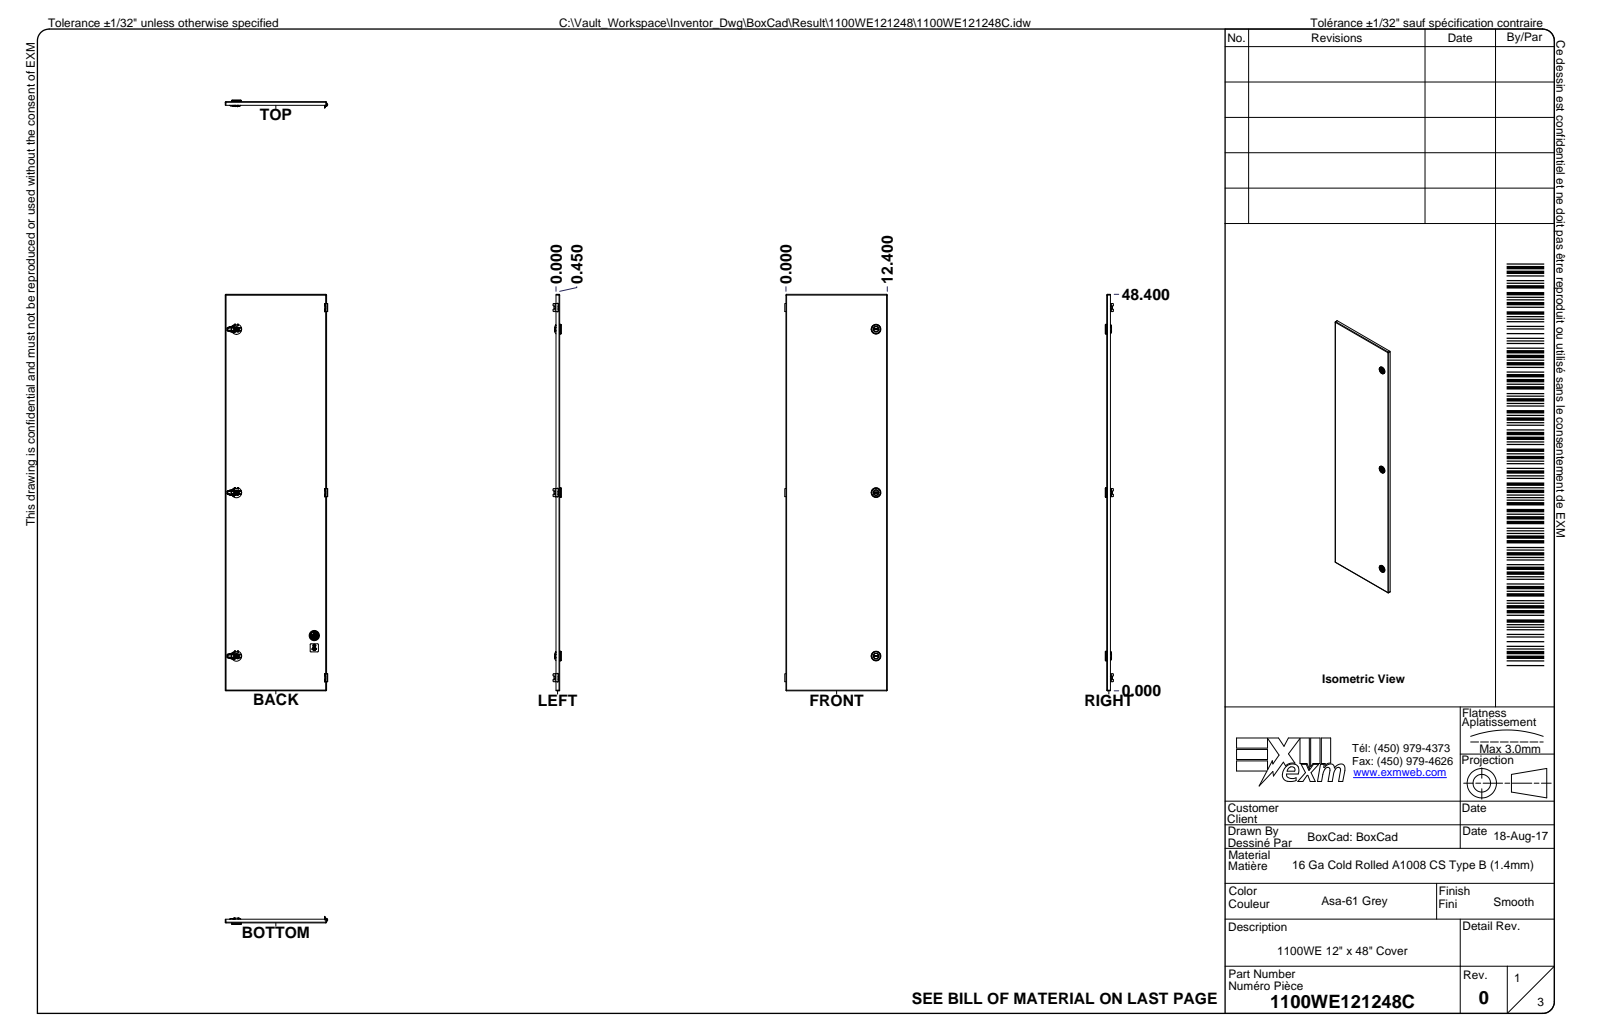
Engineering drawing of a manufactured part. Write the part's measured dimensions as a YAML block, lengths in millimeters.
part_name: "1100WE121248; 1100WE121248B; 1100WE121248B-P; 1100WE121248C (+8 more)"
step_written_by: "Autodesk Inventor 2024 (AUTOMOTIVE_DESIGN)"
units: millimeters
bodies: {solids: 13, faces: 6933, planar: 3159, cylindrical: 1487, other: 2287}
overall_size: [1229.4, 318.6, 311.1]
volume: 2456000
surface_area: 3561000
round_holes:
  - {diameter: 22.2, count: 9}
  - {diameter: 28.6, count: 9}
  - {diameter: 7.4, count: 6}
  - {diameter: 0.8, count: 4}
  - {diameter: 4.5, count: 2}
  - {diameter: 1.1, count: 1}
  - {diameter: 9.5, count: 1}
  - {diameter: 27, count: 1}
round_bosses_or_shafts:
  - {diameter: 28.6, count: 9}
  - {diameter: 22.2, count: 9}
  - {diameter: 32, count: 3}
  - {diameter: 30, count: 3}
  - {diameter: 20, count: 3}
  - {diameter: 31.8, count: 1}
  - {diameter: 29, count: 1}
  - {diameter: 7.9, count: 1}
partial_cylinders:
  - {radius: 0.3, count: 557}
  - {radius: 0.5, count: 55}
  - {radius: 2, count: 30}
  - {radius: 0.8, count: 22}
  - {radius: 0.2, count: 19}
  - {radius: 2.2, count: 14}
  - {radius: 1, count: 10}
  - {radius: 0.6, count: 9}
face_to_face_distances: [1.4, 303.4, 1.3, 304.8, 302, 305.2, 306.5, 303.8, 305.1, 1217.8]
hole_center_spacings: [152.4, 304.8, 457.2, 584.2, 609.6, 637, 254, 762]
